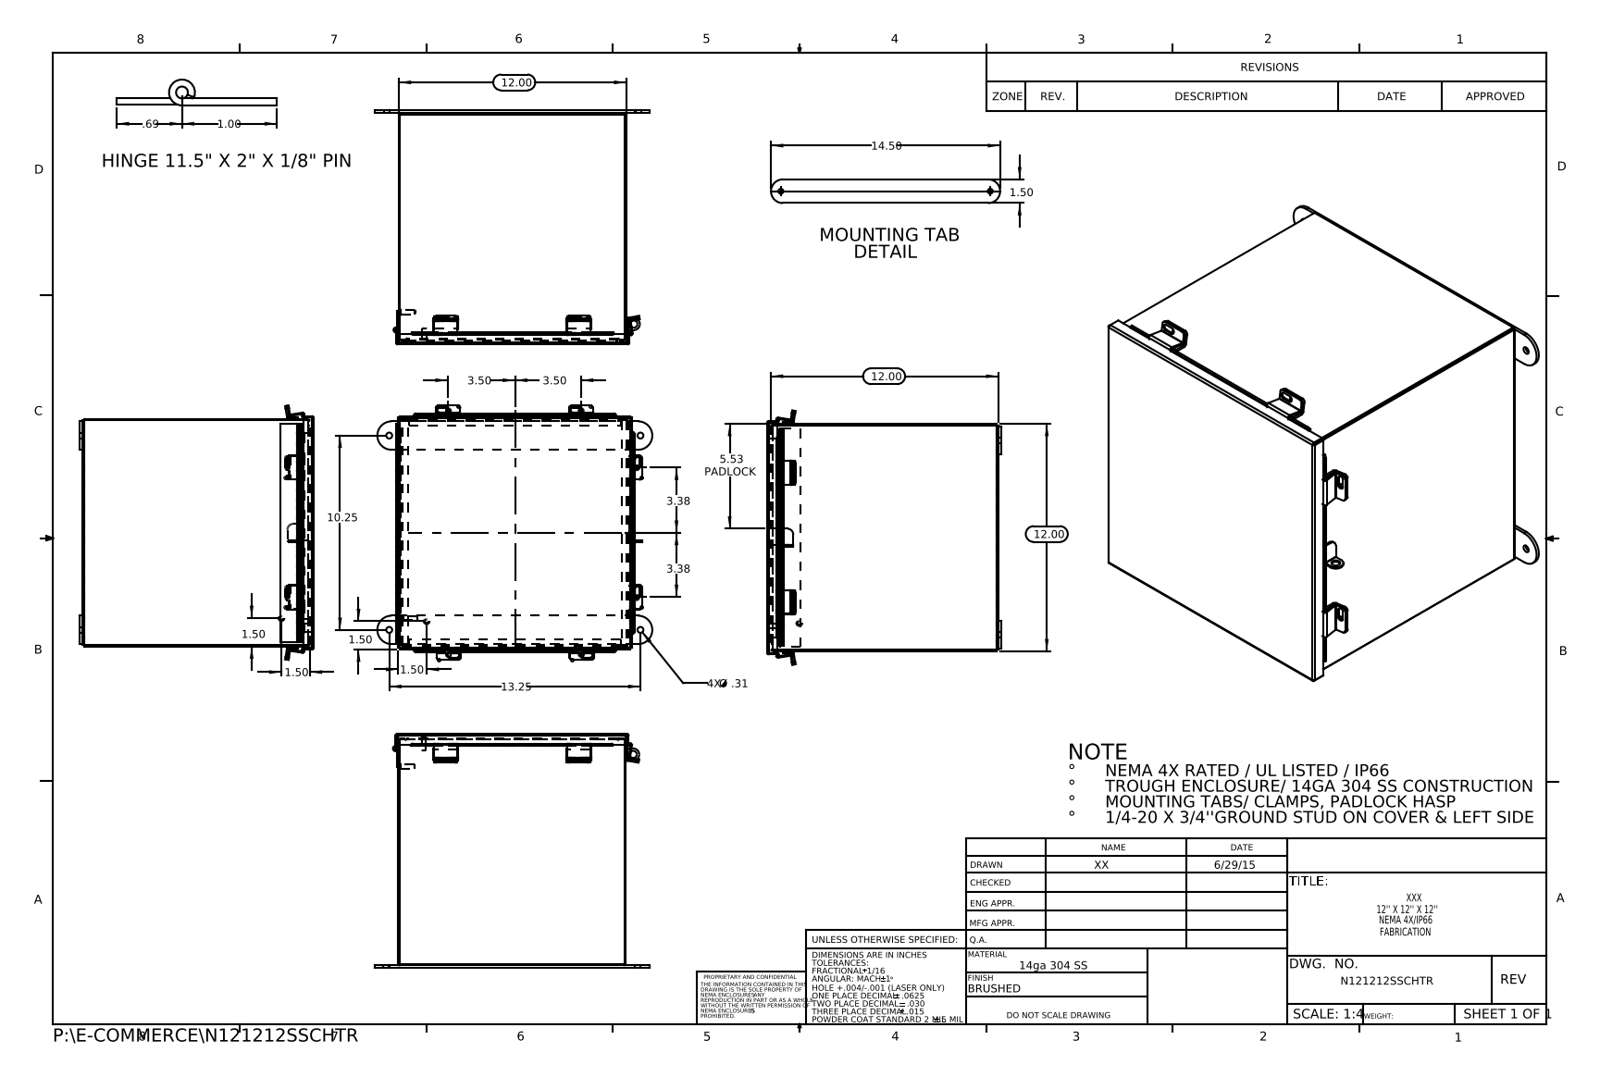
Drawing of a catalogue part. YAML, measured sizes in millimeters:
part_name: "N121212SSCHTR JIC Cover Clamp; N121212SSCHTR Hinge Body Side; N121212SSCHTR JIC Top; N121212SSCHTR JIC Enclosure Template (+8 more)"
step_written_by: "SolidWorks 2015 (CONFIG_CONTROL_DESIGN)"
units: millimeters
bodies: {solids: 23, faces: 716, planar: 457, cylindrical: 239, other: 20}
overall_size: [368.3, 340.5, 313.4]
volume: 1250000
surface_area: 1297000
round_holes:
  - {diameter: 6.4, count: 6}
  - {diameter: 8, count: 4}
  - {diameter: 3.2, count: 1}
  - {diameter: 9.5, count: 1}
round_bosses_or_shafts:
  - {diameter: 8, count: 2}
  - {diameter: 6, count: 2}
  - {diameter: 6.9, count: 1}
  - {diameter: 6.4, count: 1}
partial_cylinders:
  - {radius: 3.2, count: 24}
  - {radius: 0.2, count: 12}
  - {radius: 3.4, count: 12}
  - {radius: 0.3, count: 11}
  - {radius: 2.2, count: 11}
  - {radius: 2.1, count: 6}
  - {radius: 2.5, count: 6}
  - {radius: 19.1, count: 4}
face_to_face_distances: [1.9, 302.9, 301, 304.8, 308.1, 310, 306.1, 3.4, 5.3, 311.5]
hole_center_spacings: [177.8, 260.4, 336.6, 425.5, 174, 318.5]
